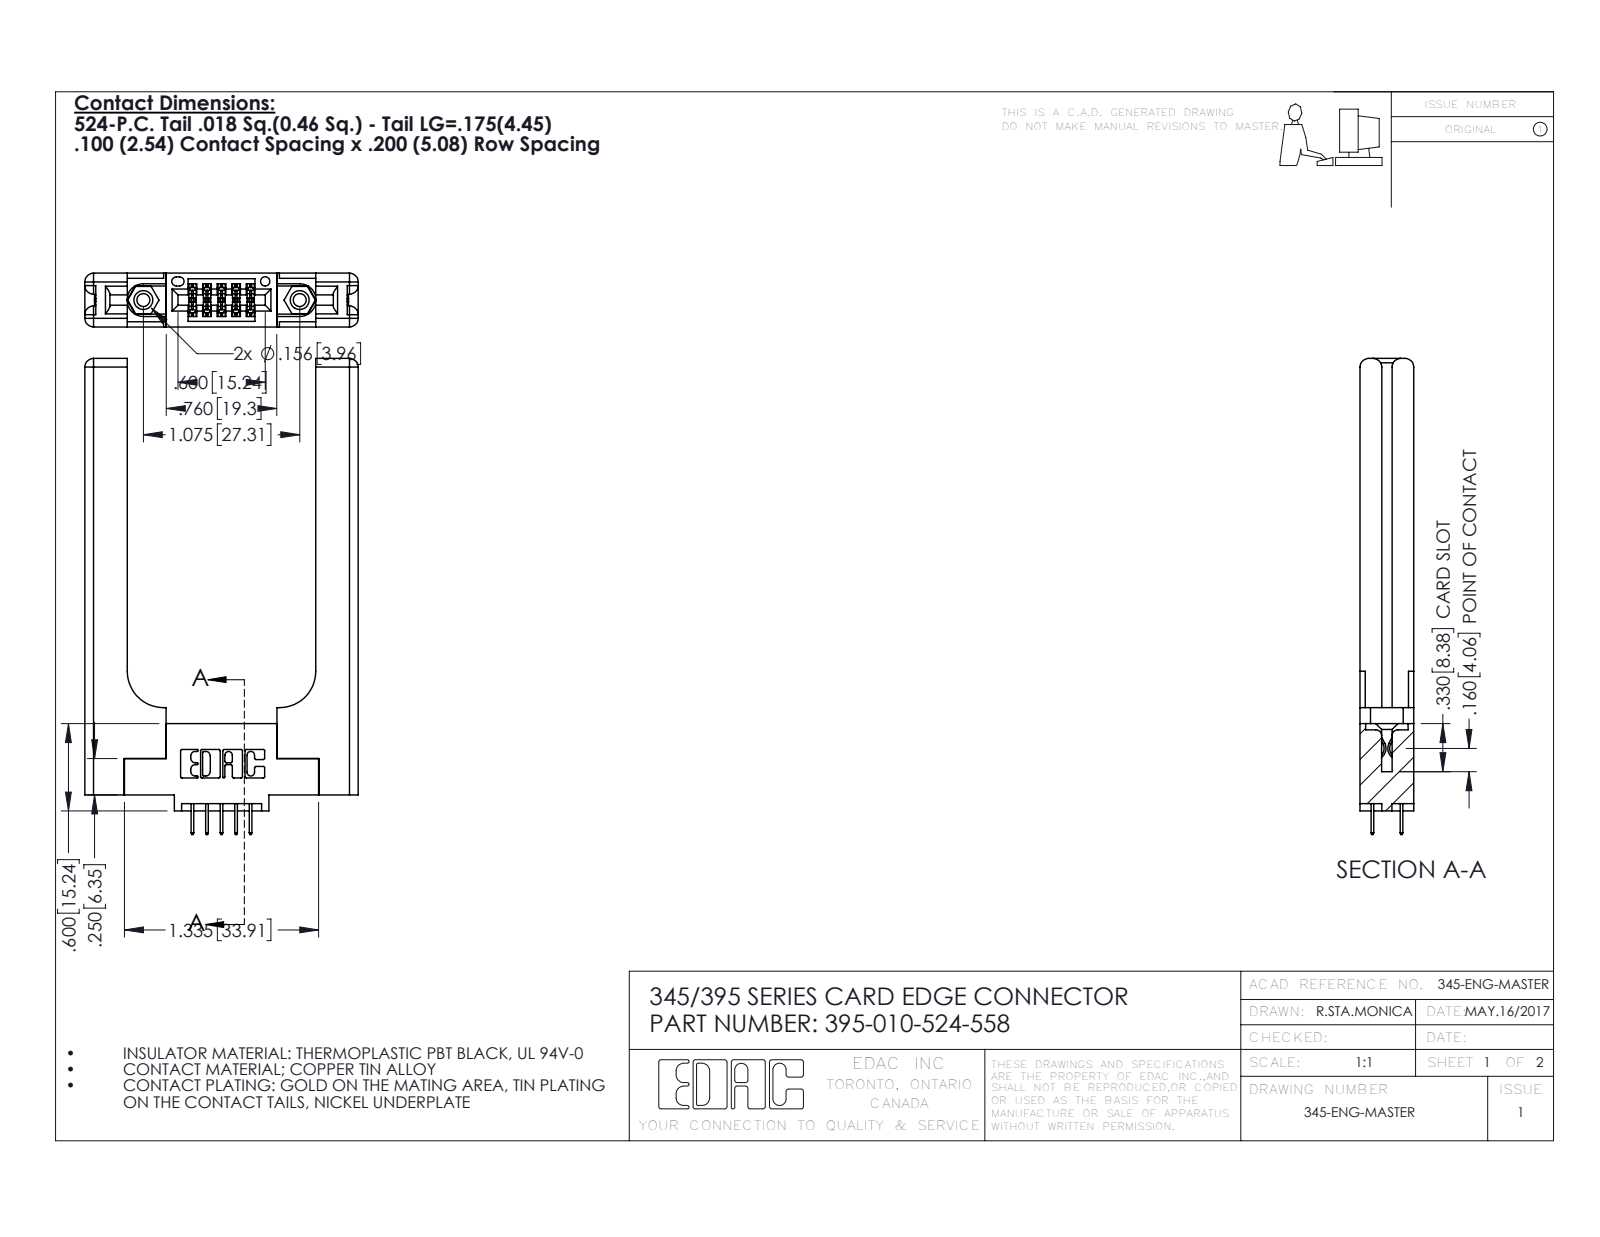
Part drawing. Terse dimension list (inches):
name: 345-250-001_345-250-001-102; 345-220-058_345-220-058; 345 Part_0.110 Offset - 0.156 Dia-TH; 395-010-524-558 (+1 more)
written by: SolidWorks 2016 (CONFIG_CONTROL_DESIGN)
unit: in
bodies: 15 solids, 926 faces (622 planar, 244 cylindrical, 60 other)
size: 3.272 × 1.879 × 0.37
volume: 0.774 in³; area: 16.45 in²
holes: 2× ⌀0.089, 2× ⌀0.125, 2× ⌀0.156, 1× ⌀0.064
bosses: 2× ⌀0.155
rounds: 22× R0.01, 16× R0.06, 15× R0.006, 6× R0.007, 6× R0.031, 3× R0.026, 2× R0.014, 2× R0.019
face distances: 0.37, 0.15, 0.22, 0.072, 1.296, 0.071, 0.148, 0.077, 0.298, 0.292
hole spacings: 0.27, 0.847, 1.075
